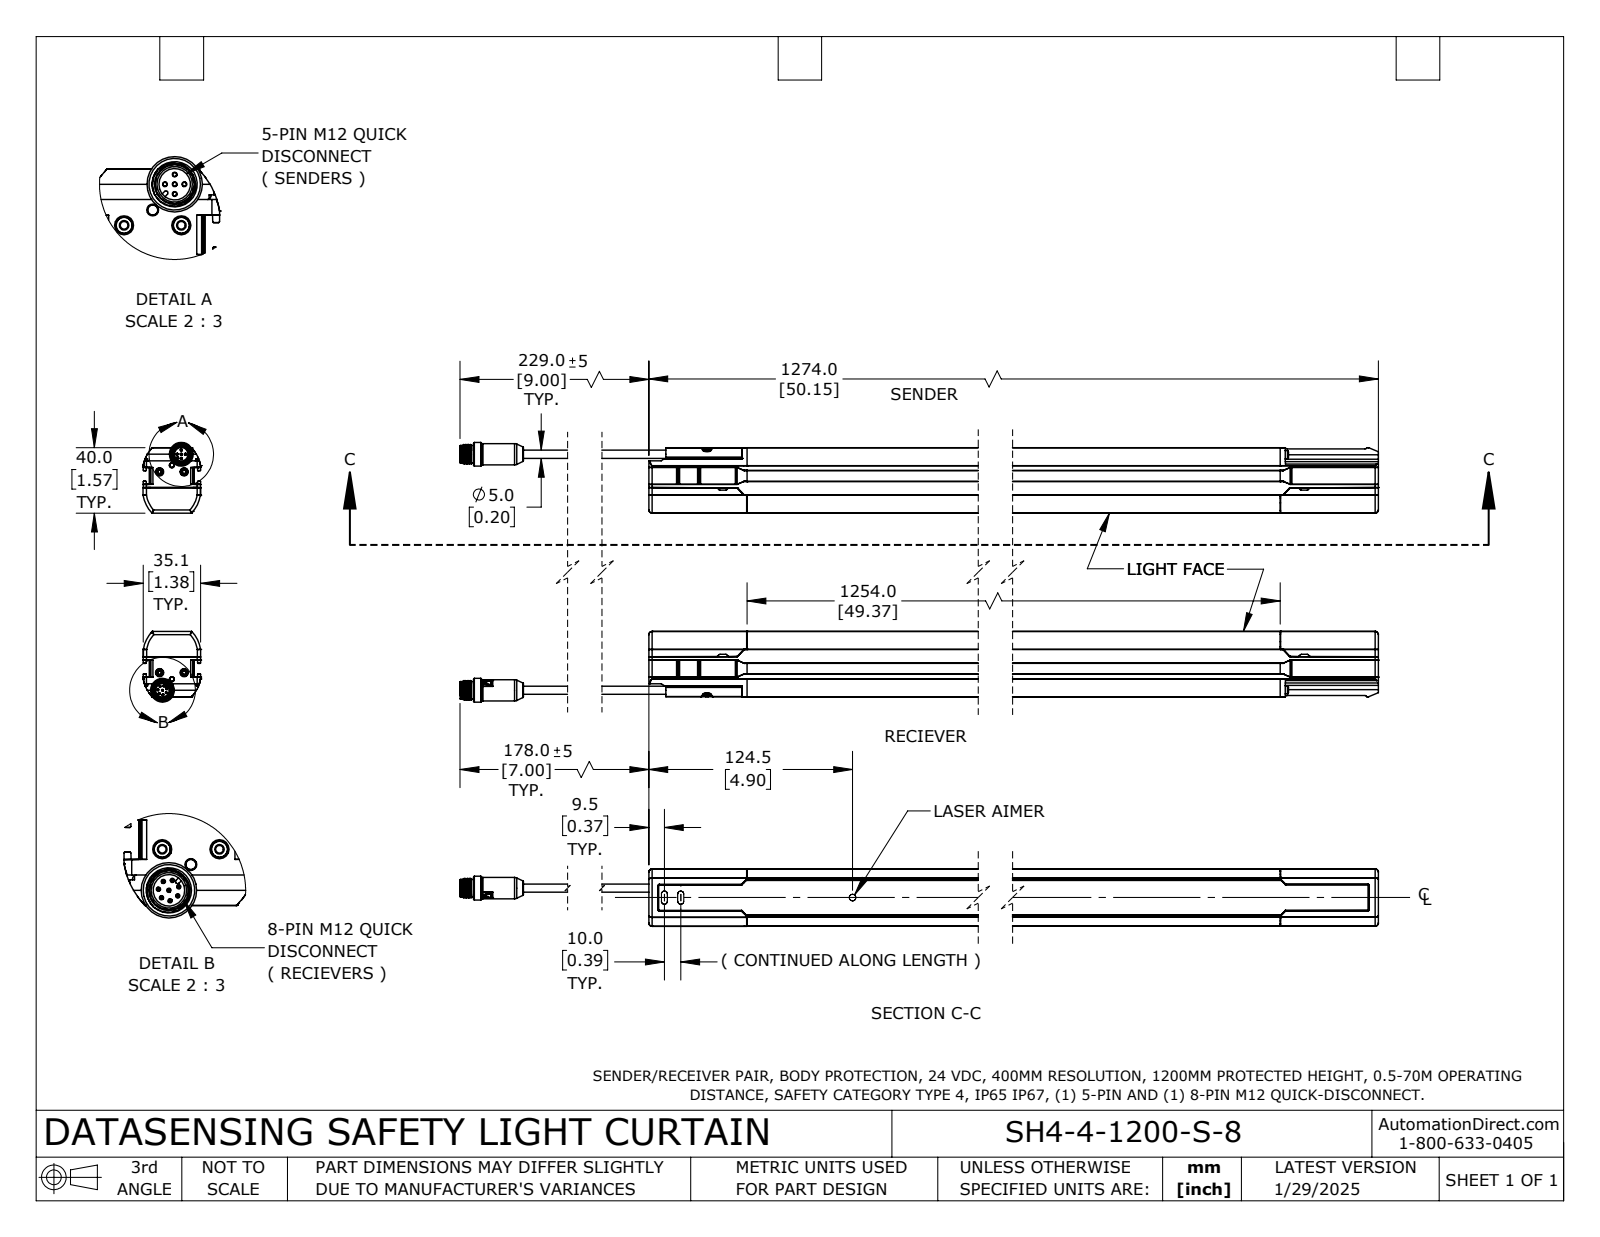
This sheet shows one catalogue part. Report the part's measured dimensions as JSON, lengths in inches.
{"part_name": "SH4-4-1200-S-8", "step_written_by": "SolidWorks 2024 (AUTOMOTIVE_DESIGN)", "units": "inches", "bodies": {"solids": 4, "faces": 2640, "planar": 1204, "cylindrical": 784, "other": 652}, "overall_size": [63.083, 6.248, 1.384], "volume_in3": 198.2, "surface_area_in2": 844.5, "round_holes": [[0.079, 4], [0.118, 4], [0.197, 4], [0.079, 2], [0.325, 2], [0.382, 2], [0.407, 2], [0.425, 2], [0.11, 1], [0.138, 1]], "round_bosses_or_shafts": [[0.197, 10], [0.087, 8], [0.031, 8], [0.039, 5], [0.172, 4], [0.571, 2], [0.512, 2], [0.417, 2]], "partial_cylinders_radius": [[0.01, 164], [0.016, 66], [0.02, 50], [0.008, 36], [0.031, 20], [0.031, 12], [0.079, 12], [0.059, 10]], "face_to_face_distances": [1.496, 4.496, 0.156, 1.222, 3, 5.992, 1.378, 1.067, 4.634, 0.069], "hole_center_spacings": [0.429, 0.591, 0.672, 4.831, 4.867, 5.254, 5.28, 5.695]}
